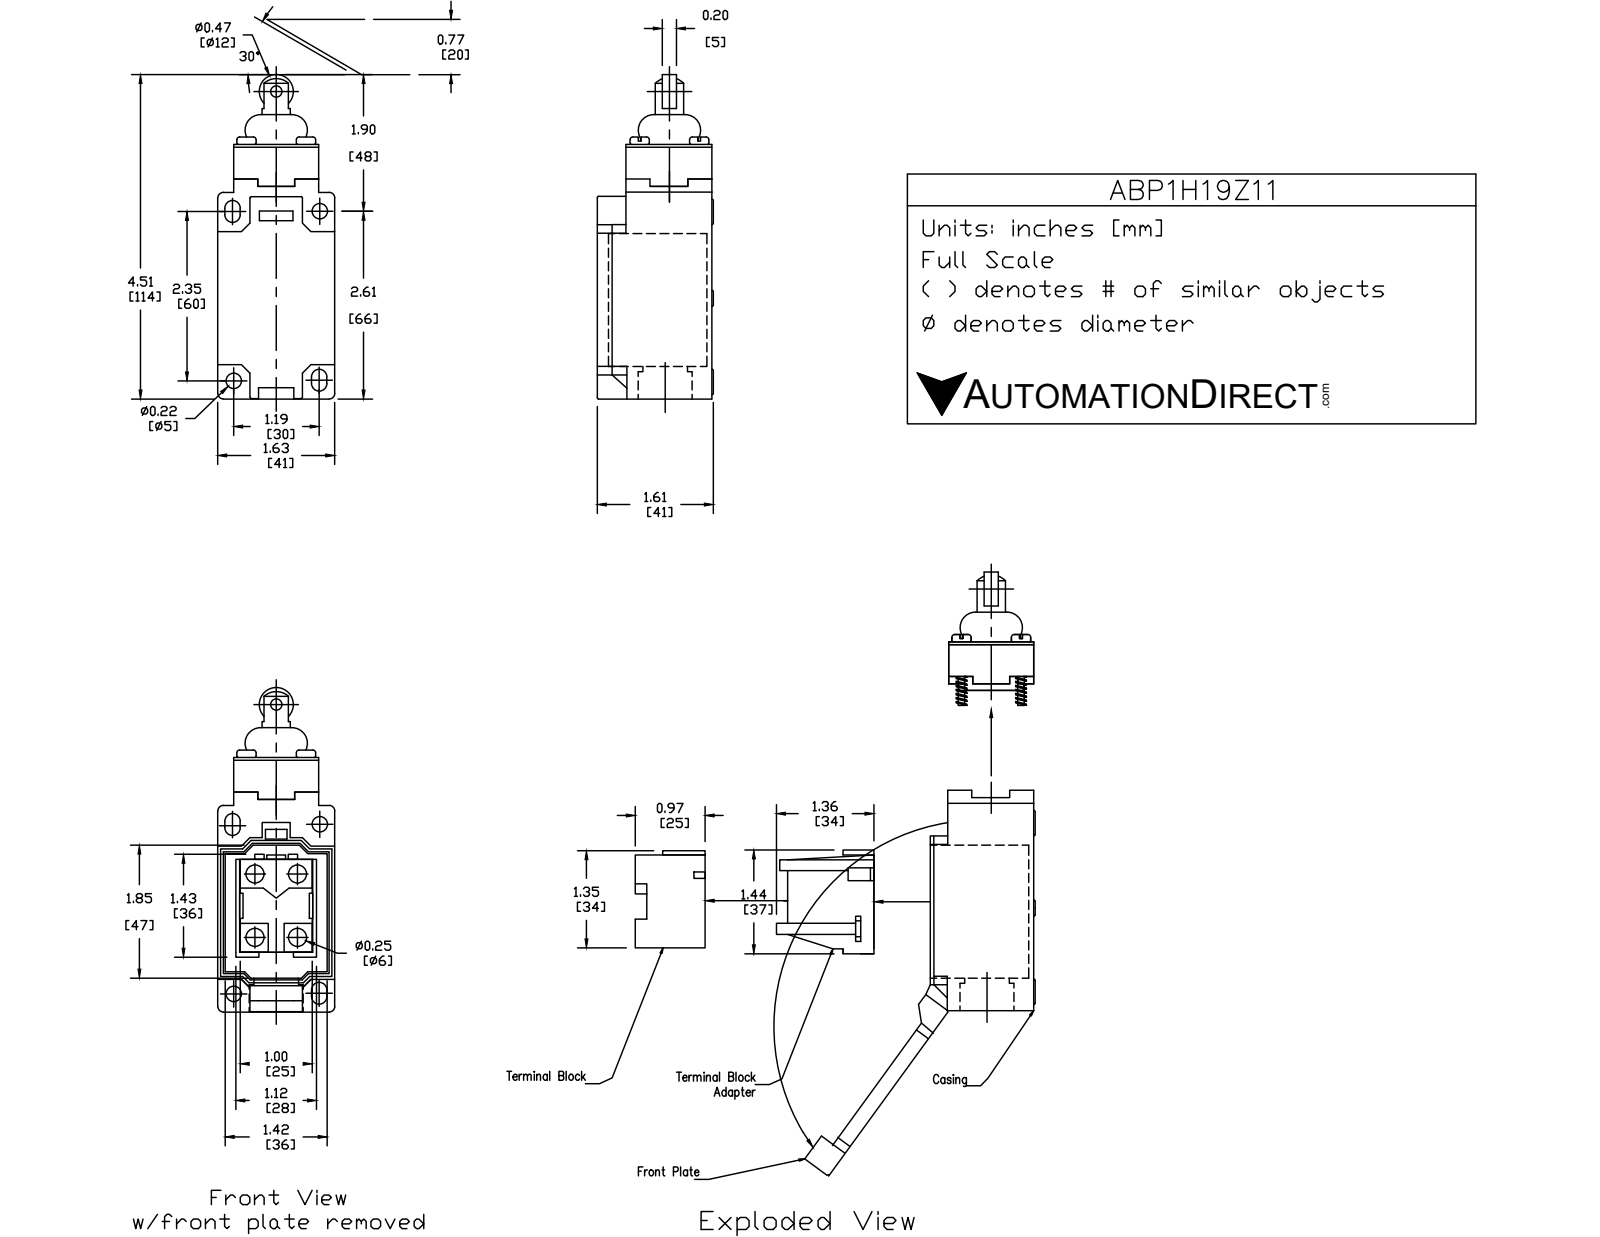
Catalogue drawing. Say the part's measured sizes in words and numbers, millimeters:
The part is named "ABP1H19Z11". Its 3-D file was written by "SolidWorks 2017 (AUTOMOTIVE_DESIGN)". It is 4 solids with 188 faces: 86 planar, 76 cylindrical and 26 other. Overall it measures 116.7 by 41 by 40.3 millimeters. Its volume is 127 500 cubic millimeters and its surface area 25 070 square millimeters. Round holes: 2 of diameter 5.4, 1 of diameter 10.1, 1 of diameter 17, 1 of diameter 19, 1 of diameter 20.5. Round bosses or shafts: 4 of diameter 9, 4 of diameter 7, 1 of diameter 20, 1 of diameter 12, 1 of diameter 10. Partial cylindrical surfaces (rounded edges, fillets, slot ends): 16 of radius 0.5, 4 of radius 0.6, 4 of radius 2, 4 of radius 2.7, 1 of radius 11.5, 1 of radius 12. The main face-to-face distances are 41, 39.8, 30, 75.5, 9.8, 5.5, 35.5, 2.5, 78, 12. The hole center spacings are 1.5, 67.1.
